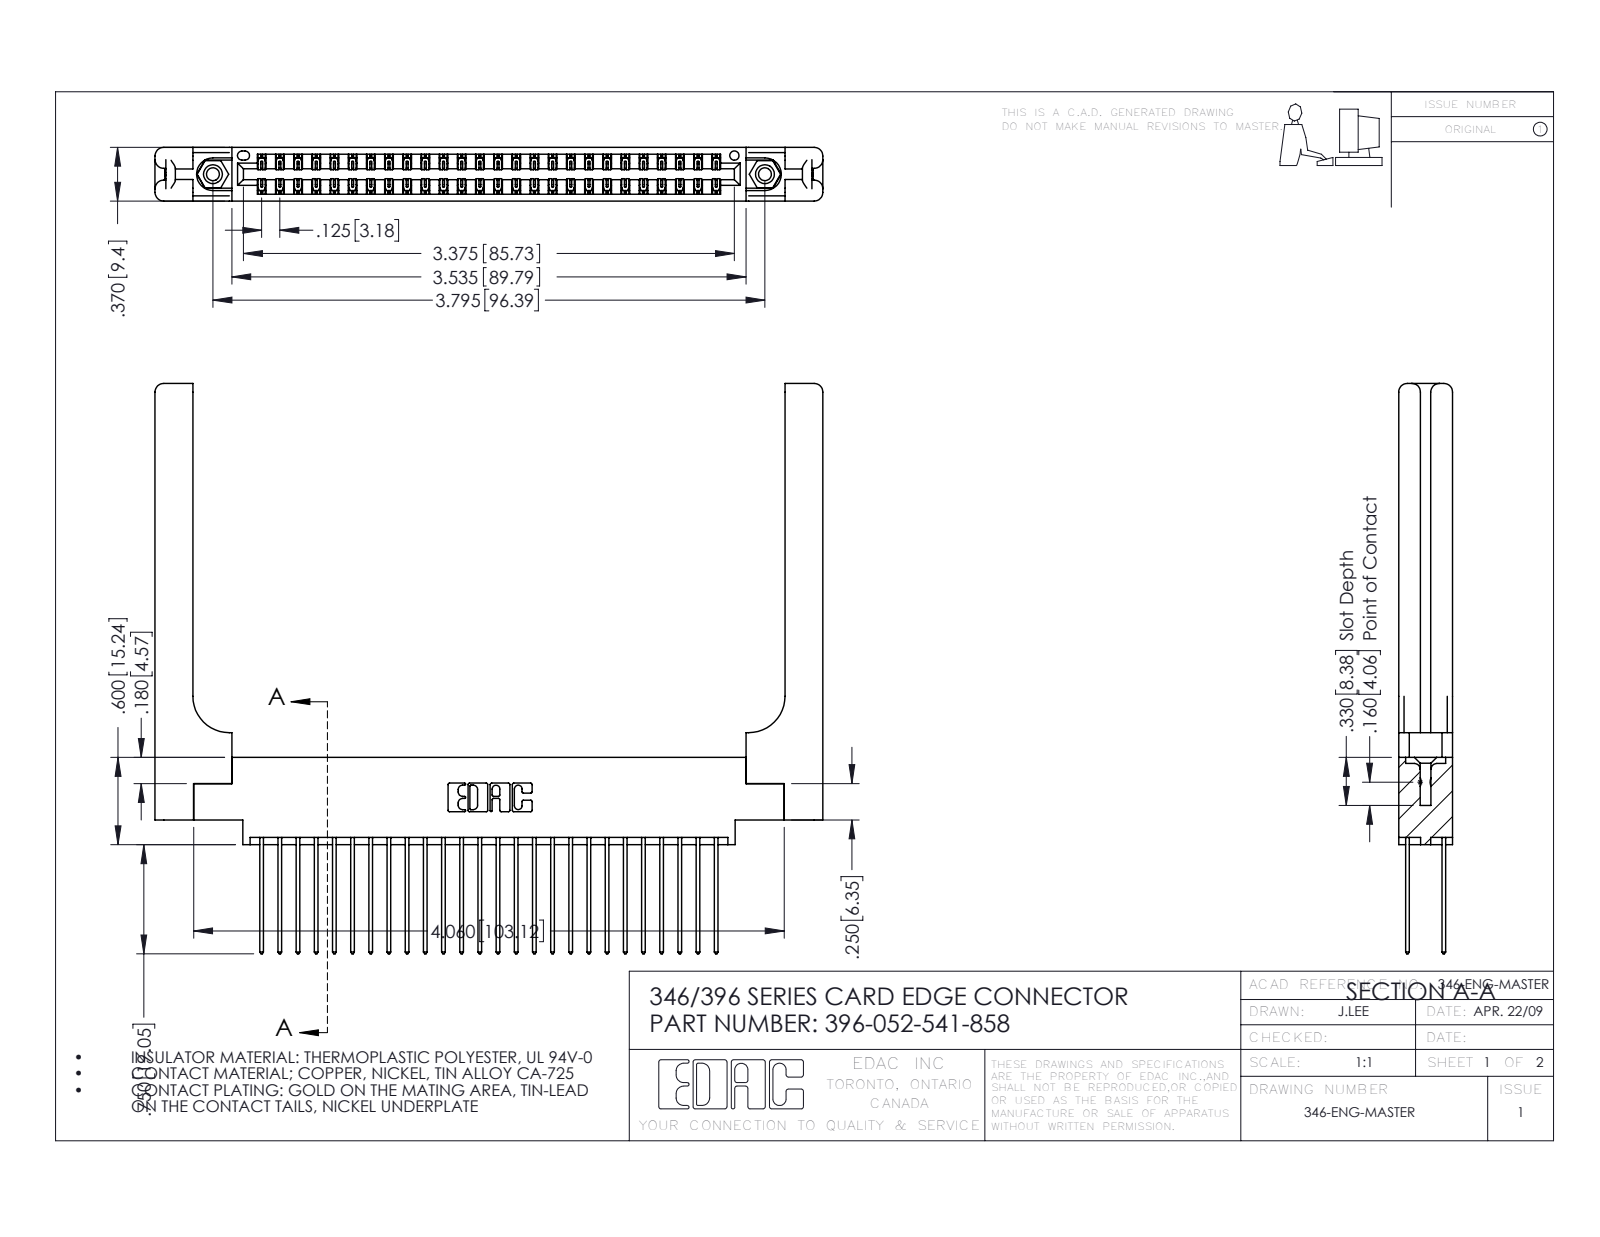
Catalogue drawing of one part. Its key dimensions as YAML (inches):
part_name: "345-292-001_345-293-141; 346-220-058_345-220-058; 345-250-001_345-250-001-102; 396-052-541-858 (+1 more)"
step_written_by: "SolidWorks 2016 (CONFIG_CONTROL_DESIGN)"
units: inches
bodies: {solids: 57, faces: 3086, planar: 2048, cylindrical: 978, other: 60}
overall_size: [4.591, 3.92, 0.37]
volume: 1.152
surface_area: 34.08
round_holes:
  - {diameter: 0.089, count: 2}
  - {diameter: 0.125, count: 2}
  - {diameter: 0.156, count: 2}
  - {diameter: 0.064, count: 1}
round_bosses_or_shafts:
  - {diameter: 0.155, count: 2}
partial_cylinders:
  - {radius: 0.006, count: 78}
  - {radius: 0.01, count: 52}
  - {radius: 0.01, count: 22}
  - {radius: 0.06, count: 16}
  - {radius: 0.007, count: 6}
  - {radius: 0.031, count: 6}
  - {radius: 0.026, count: 3}
  - {radius: 0.014, count: 2}
face_to_face_distances: [0.37, 0.072, 0.048, 0.322, 0.25, 0.025, 0.298, 0.148, 0.15, 0.275]
hole_center_spacings: [0.246, 3.587, 3.795]
